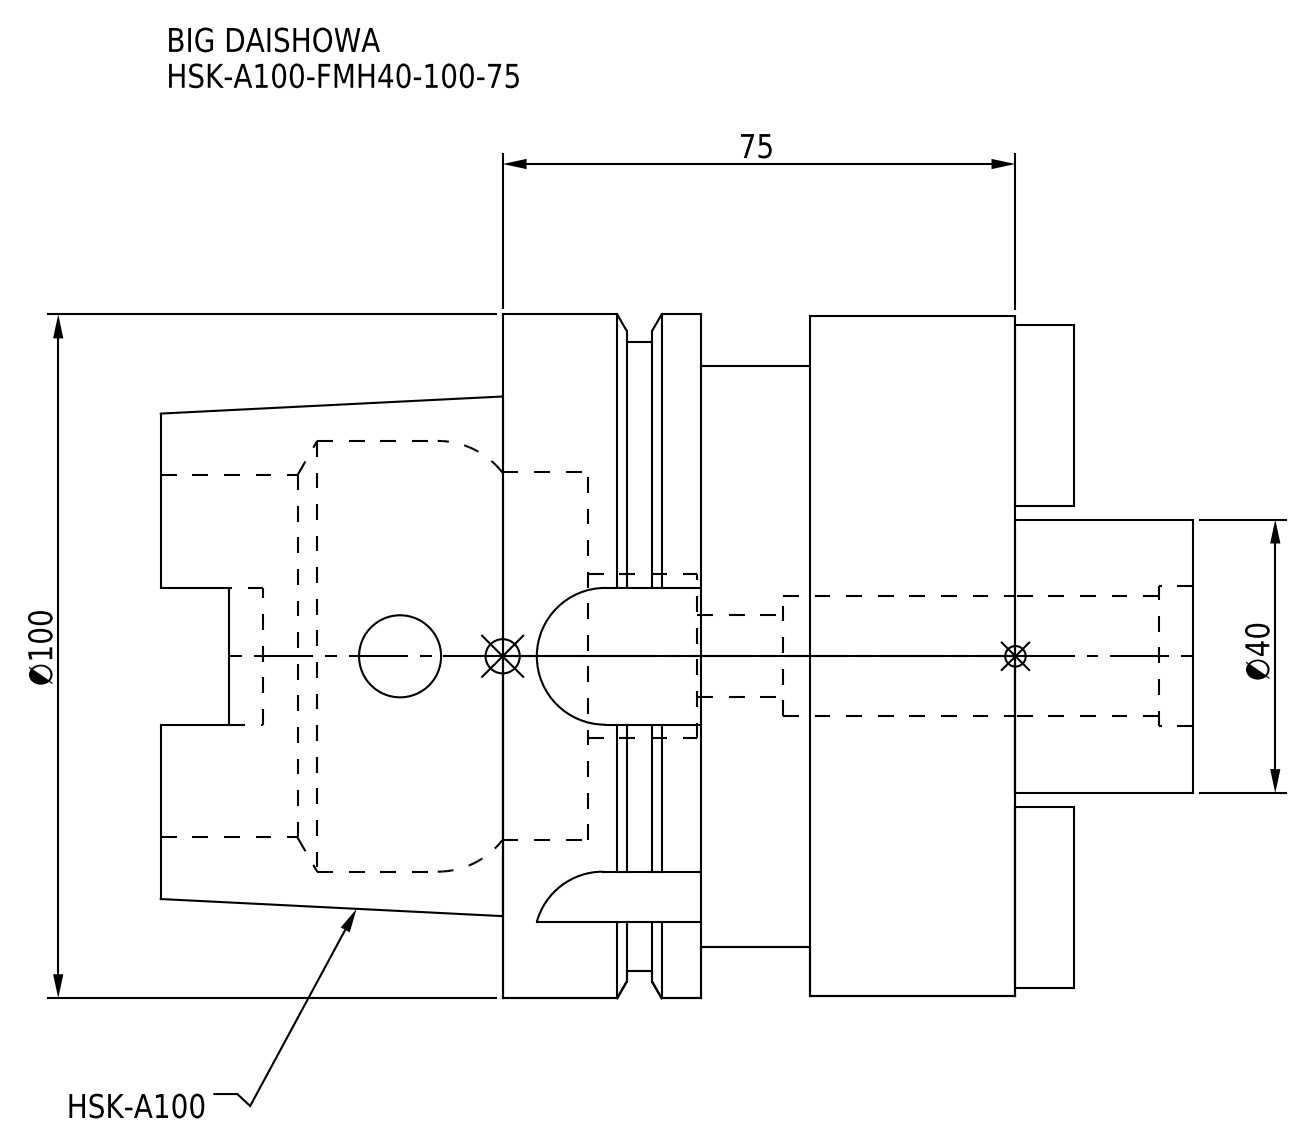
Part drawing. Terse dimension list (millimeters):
name: HSK-A100-FMH40-100-75
written by: CREO PARAMETRIC BY PTC INC, 2016380 (AUTOMOTIVE_DESIGN)
unit: mm
bodies: 1 solid, 104 faces (46 planar, 44 cylindrical, 14 other)
size: 151 × 100 × 100
volume: 601 139 mm³; area: 76 151 mm²
holes: 2× ⌀12, 1× ⌀17.5, 1× ⌀20.5, 1× ⌀24, 1× ⌀53, 1× ⌀53.8, 1× ⌀63
bosses: 1× ⌀100, 1× ⌀99.5, 1× ⌀92, 1× ⌀85, 1× ⌀40
rounds: 4× R4.88, 4× R10
face distances: 75, 16, 16.55, 45, 30, 46, 29, 62.55, 32.55, 12.45
